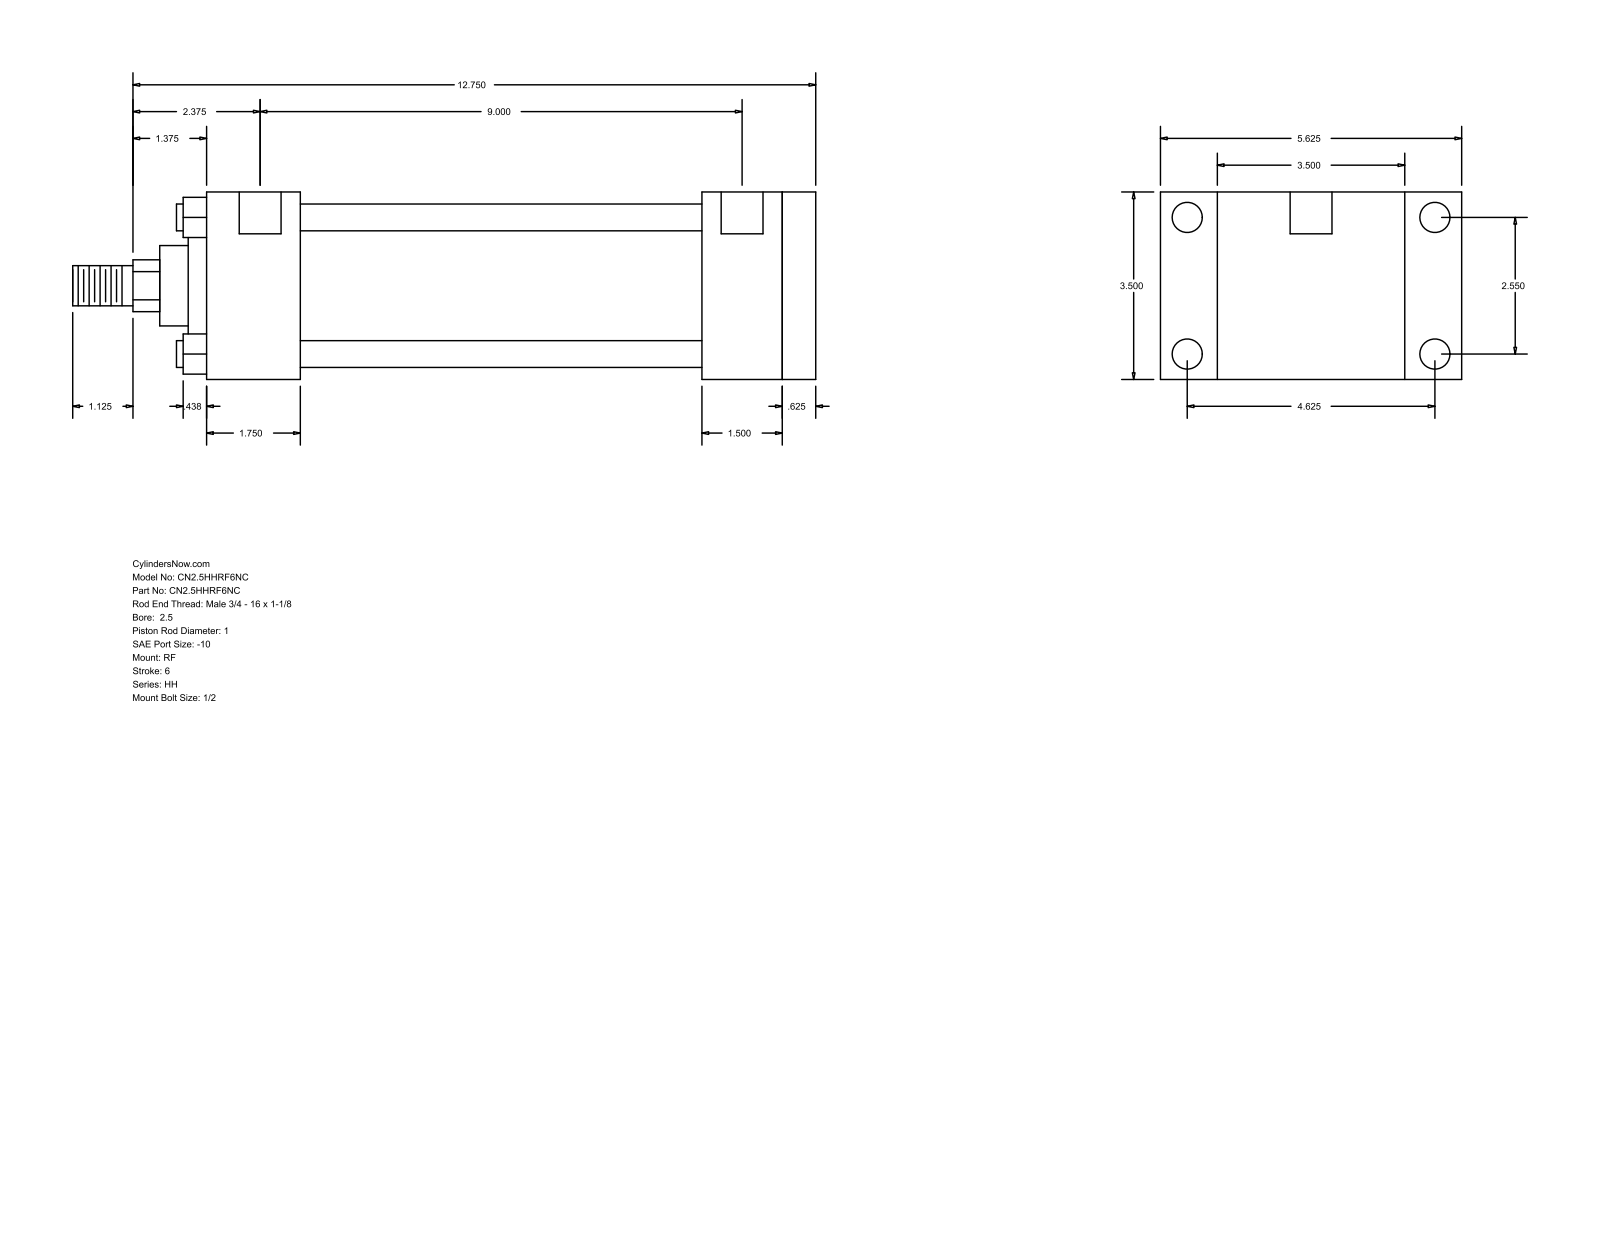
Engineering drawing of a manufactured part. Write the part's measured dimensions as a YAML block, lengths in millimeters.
part_name: "HH_RF__0250_1"
step_written_by: "GSSL Pune (CONFIG_CONTROL_DESIGN)"
units: millimeters
bodies: {solids: 0, faces: 94, planar: 65, cylindrical: 29, other: 0}
overall_size: [352.43, 142.88, 88.9]
round_holes:
  - {diameter: 5.56, count: 4}
  - {diameter: 14.3, count: 4}
  - {diameter: 19.84, count: 2}
round_bosses_or_shafts:
  - {diameter: 12.7, count: 4}
  - {diameter: 73.03, count: 1}
  - {diameter: 60.33, count: 1}
  - {diameter: 38.1, count: 1}
  - {diameter: 25.4, count: 1}
  - {diameter: 19.05, count: 1}
partial_cylinders:
  - {radius: 12.29, count: 1}
face_to_face_distances: [88.9, 15.87, 273.06, 288.93, 38.1, 44.46, 228.6, 244.47, 234.96, 190.5]
hole_center_spacings: [64.76, 117.48, 134.15, 231.77, 1.58, 1.59, 228.6, 230.18]
